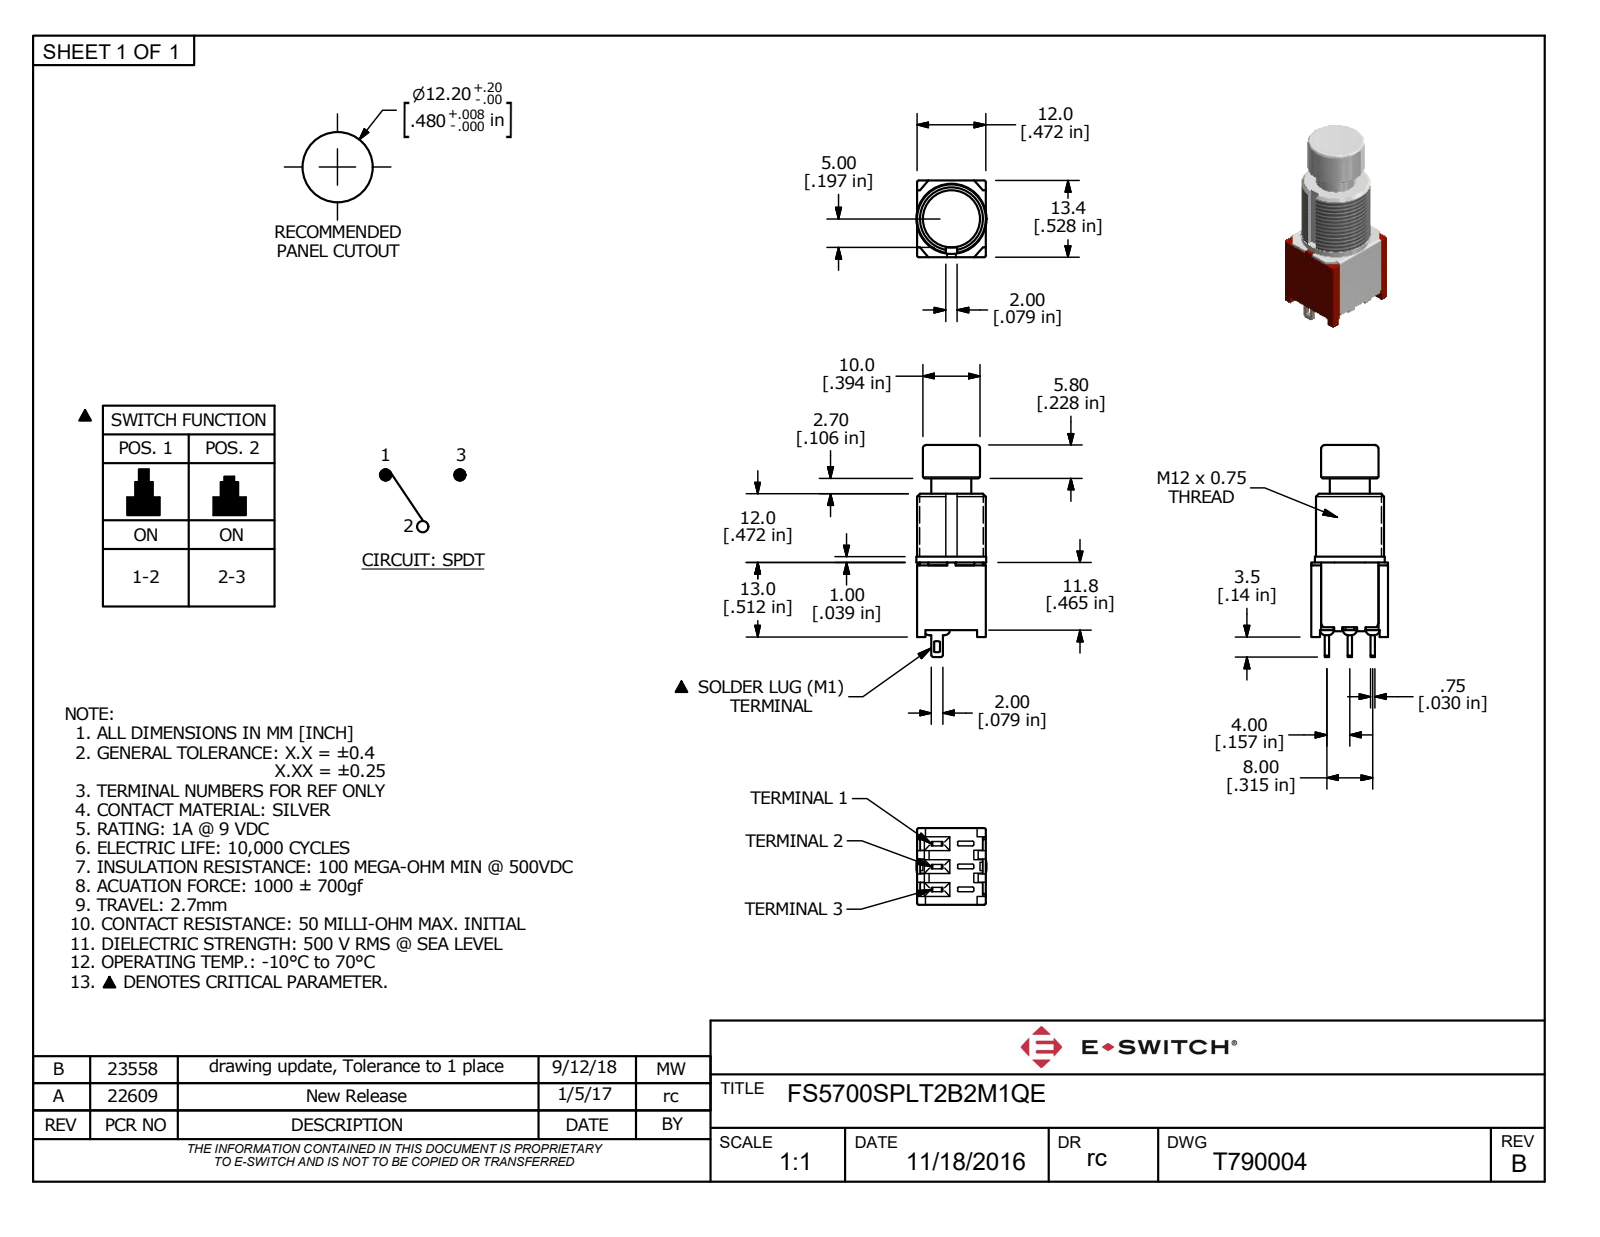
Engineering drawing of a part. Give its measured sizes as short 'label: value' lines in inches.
name: FS5700SPLT2B2M1QE
written by: Autodesk Inventor 2022 (AUTOMOTIVE_DESIGN)
unit: in
bodies: 1 solid, 280 faces (212 planar, 65 cylindrical, 3 other)
size: 1.457 × 0.528 × 0.48
volume: 0.128 in³; area: 5.084 in²
holes: 1× ⌀0.354
bosses: 1× ⌀0.48, 1× ⌀0.472, 1× ⌀0.394, 1× ⌀0.276
rounds: 26× R0.008, 8× R0.035, 4× R0.012, 4× R0.02, 2× R0.004, 1× R0.039
face distances: 0.047, 0.02, 0.433, 0.425, 0.406, 0.028, 0.453, 0.022, 0.451, 0.026
